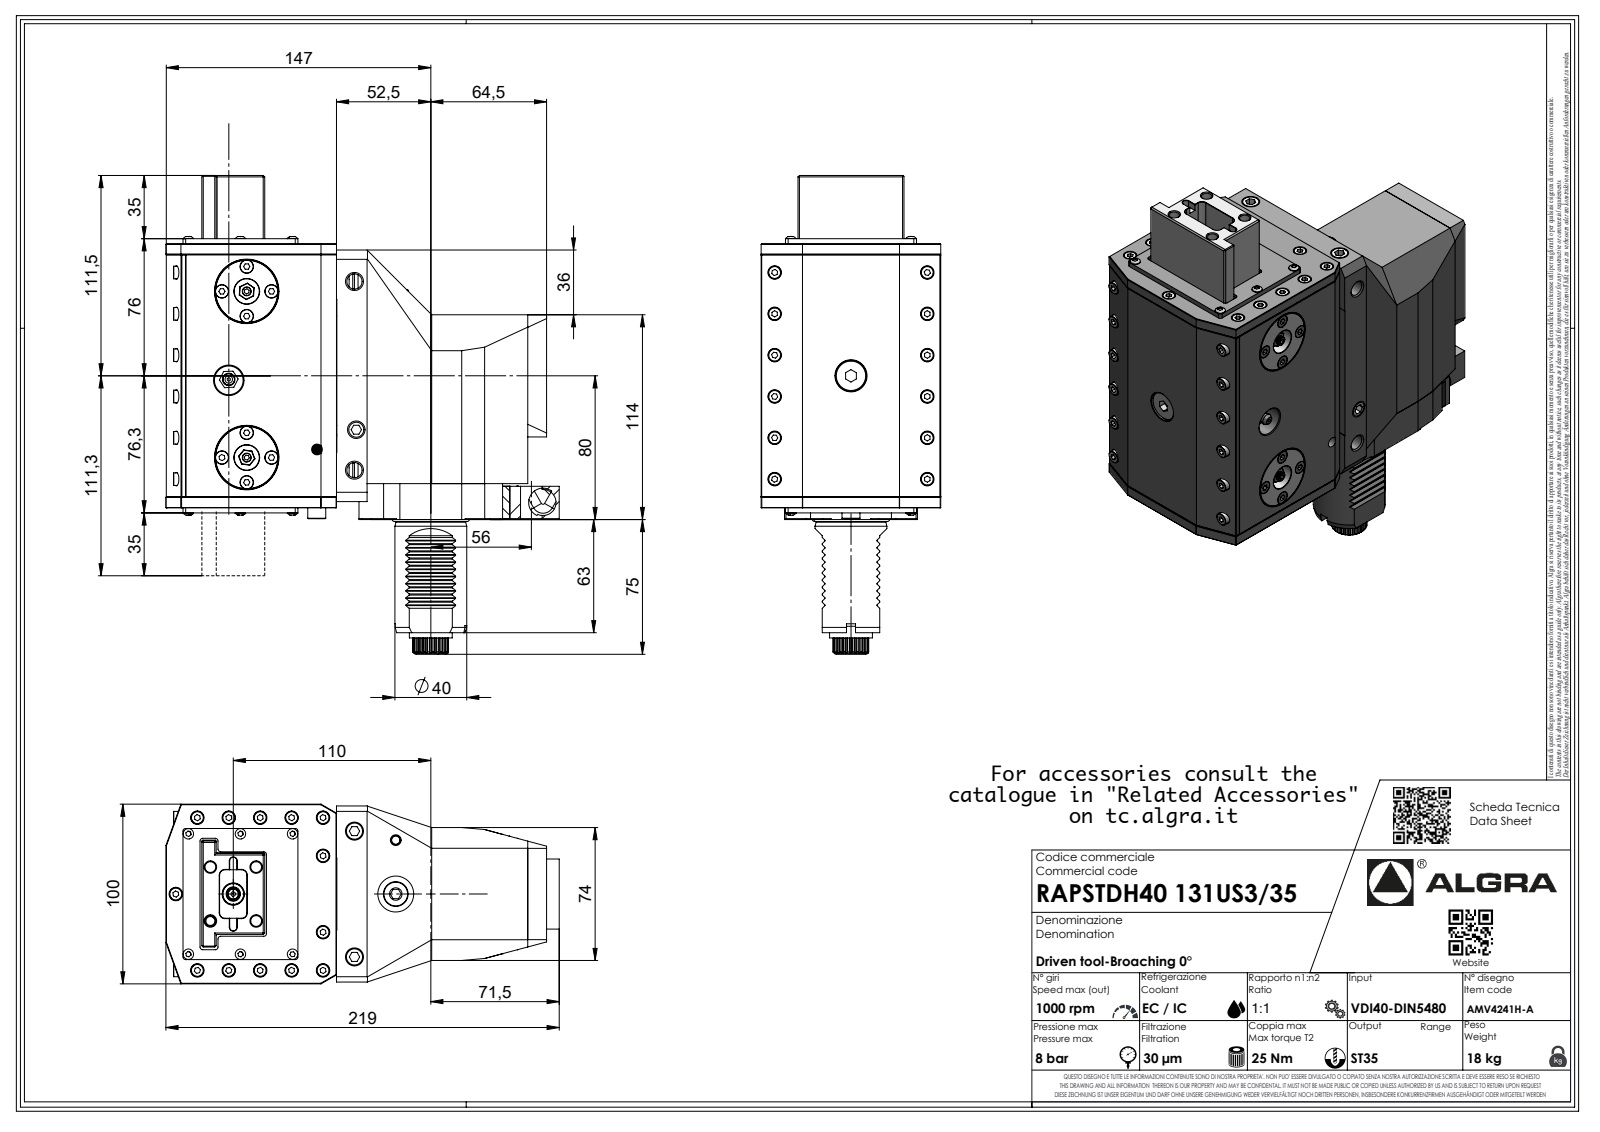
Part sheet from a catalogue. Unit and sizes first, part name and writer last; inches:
Units: inches
Overall size (bounding box): 10.492 × 8.465 × 3.937
Round holes (diameter × count): ⌀0.124 ×1, ⌀0.157 ×1, ⌀1.024 ×1, ⌀1.197 ×1
Round bosses / shafts (diameter × count): ⌀1.575 ×1, ⌀1.524 ×1, ⌀0.689 ×1, ⌀0.376 ×1, ⌀0.236 ×1, ⌀0.1 ×1
Partial cylindrical surfaces — rounded edges, fillets, slot ends (radius × count): R0.012 ×20, R0.02 ×10, R0.02 ×7, R0.031 ×7, R0.219 ×7, R0.059 ×4, R0.118 ×4, R0.236 ×4
Main face-to-face distances: 3.937, 0.11, 5.898, 0.472, 0.039, 4.232, 3.898, 0.256, 5.787, 0.512
Volume: 157.7 in³ · Surface area: 219.1 in²
Bodies: 1 solid, 921 faces (630 planar, 109 cylindrical, 182 other)
Part name (STEP PRODUCT): RAPSTDH40131US335
STEP written by: SolidWorks 2016 (AUTOMOTIVE_DESIGN)
